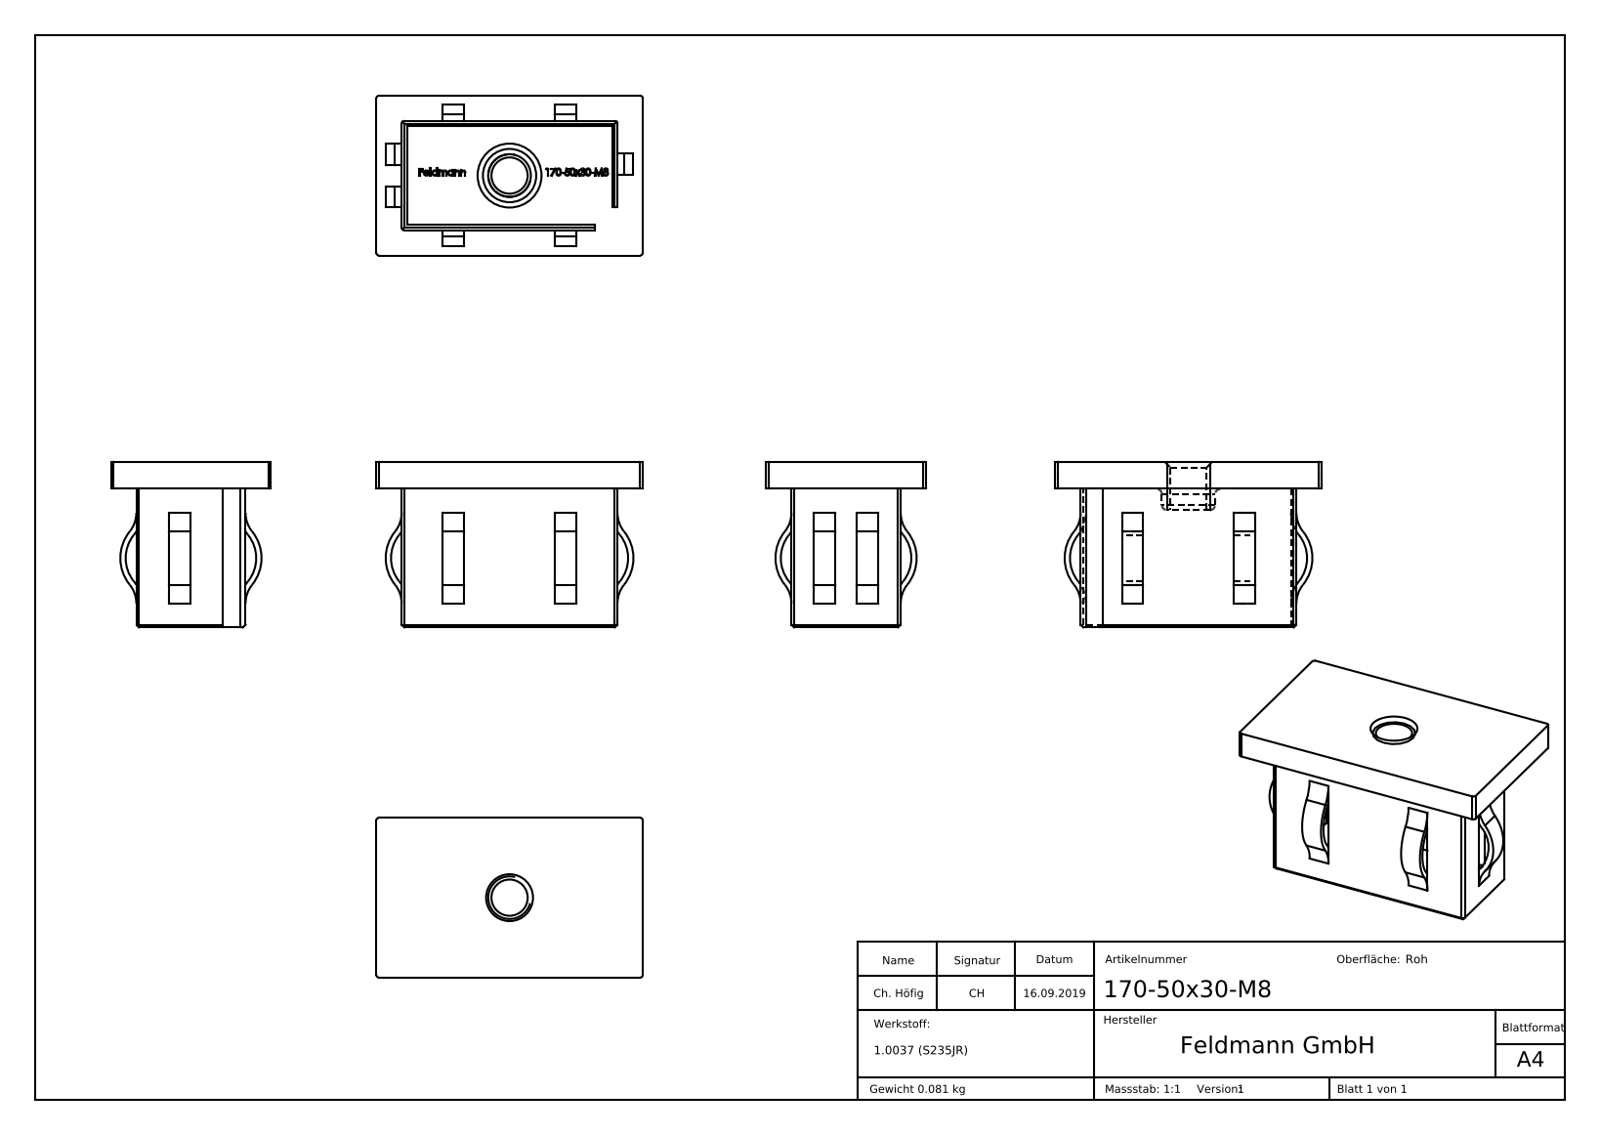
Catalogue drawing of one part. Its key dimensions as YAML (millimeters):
part_name: "170-50x30-M8"
step_written_by: "SolidWorks 2015 (CONFIG_CONTROL_DESIGN)"
units: millimeters
bodies: {solids: 1, faces: 367, planar: 186, cylindrical: 61, other: 120}
overall_size: [50, 31, 30]
volume: 10368
surface_area: 10202
round_holes:
  - {diameter: 6.8, count: 1}
round_bosses_or_shafts:
  - {diameter: 10, count: 1}
partial_cylinders:
  - {radius: 5.58, count: 8}
  - {radius: 6.58, count: 8}
  - {radius: 0.5, count: 7}
  - {radius: 6.97, count: 4}
  - {radius: 7.97, count: 4}
face_to_face_distances: [1, 19.5, 5, 18.5, 4.75, 5.75, 20.5, 39.5, 24.25, 25.25]
